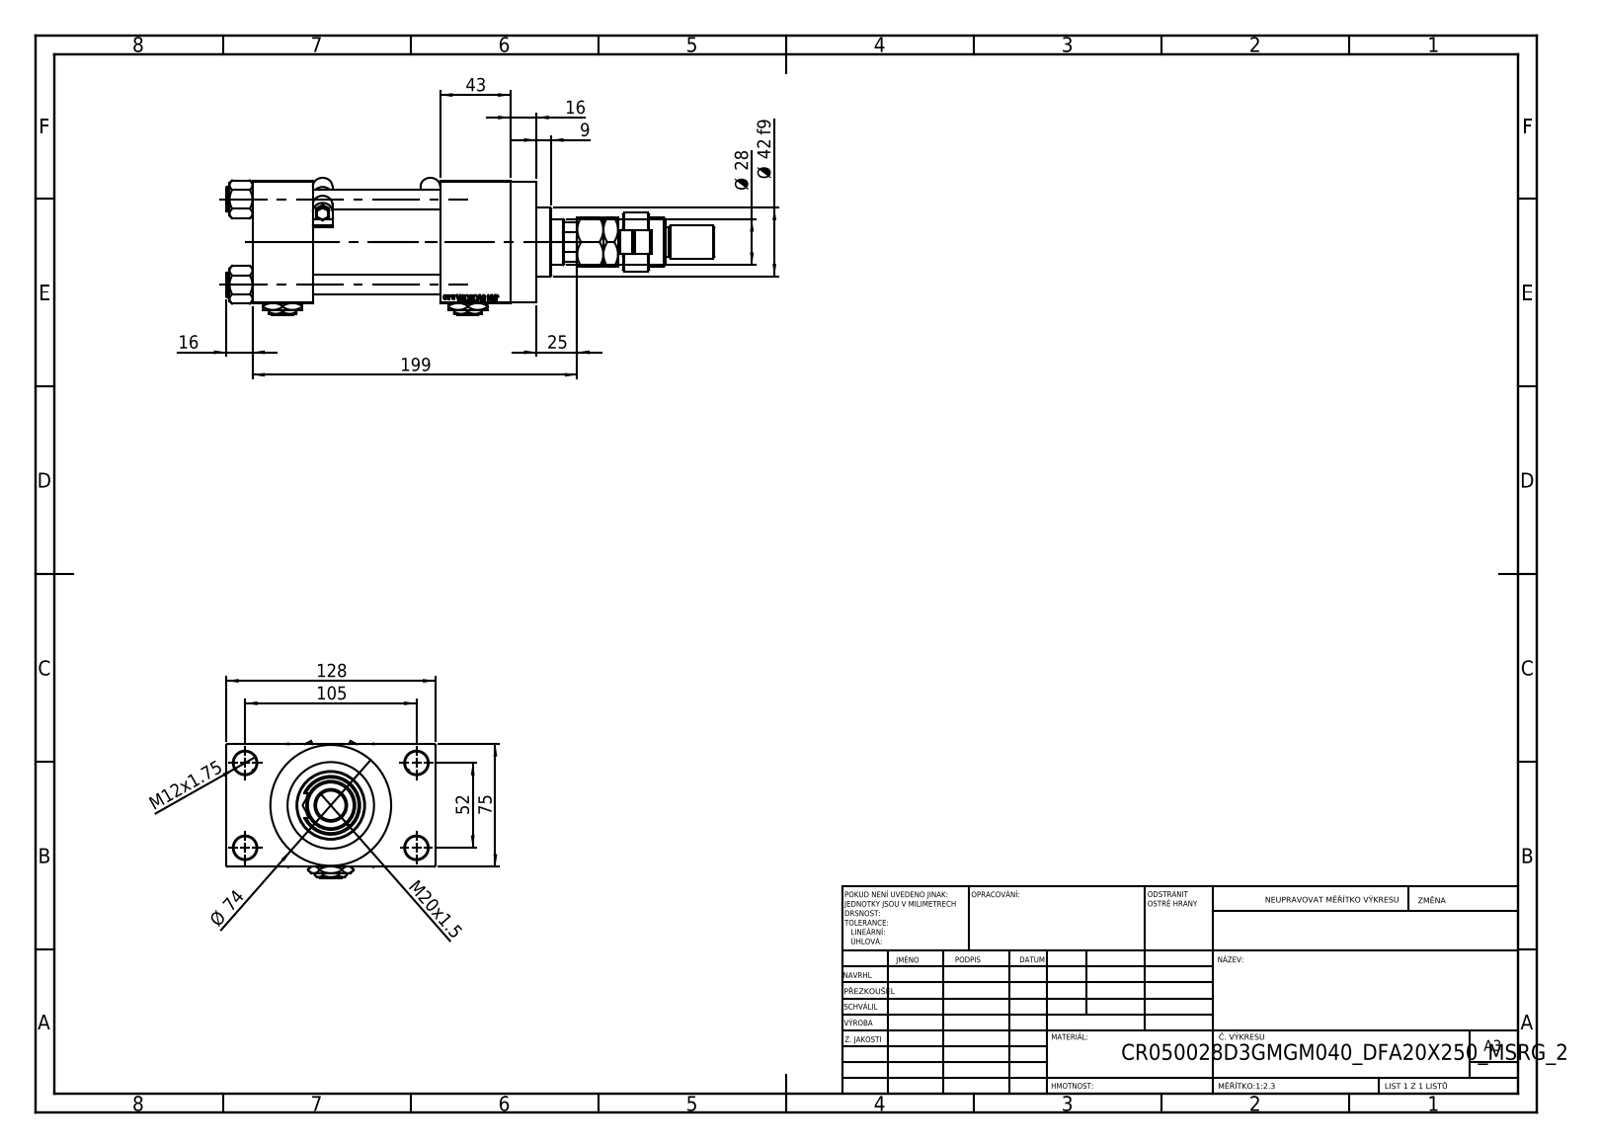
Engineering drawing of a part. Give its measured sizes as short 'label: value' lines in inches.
name: MFA; FEMALE_PART_FOR_DFA; Zatka_pro_OIL_PORT; MSRF_MSRG1 (+5 more)
written by: SolidWorks 2019 (CONFIG_CONTROL_DESIGN)
unit: in
bodies: 17 solids, 1353 faces (609 planar, 140 cylindrical, 604 other)
size: 11.772 × 5.039 × 3.302
volume: 54.3 in³; area: 316 in²
holes: 4× ⌀0.472, 4× ⌀0.551, 4× ⌀0.825, 4× ⌀1.181, 3× ⌀0.276, 1× ⌀0.728, 1× ⌀1.102, 1× ⌀1.22, 1× ⌀1.614, 1× ⌀1.969, 1× ⌀2.087
bosses: 4× ⌀0.591, 2× ⌀0.197, 2× ⌀0.098, 1× ⌀2.913, 1× ⌀2.205, 1× ⌀1.654, 1× ⌀1.417, 1× ⌀1.181
rounds: 12× R0.02, 4× R0.236, 1× R0.295, 1× R0.472, 1× R0.531
face distances: 2.953, 3.071, 1.457, 4.528, 1.043, 4.764, 1.693, 6.22, 3.996, 0.63
hole spacings: 1.037, 1.456, 2.059, 2.3, 2.307, 3.096, 3.715, 2.047
